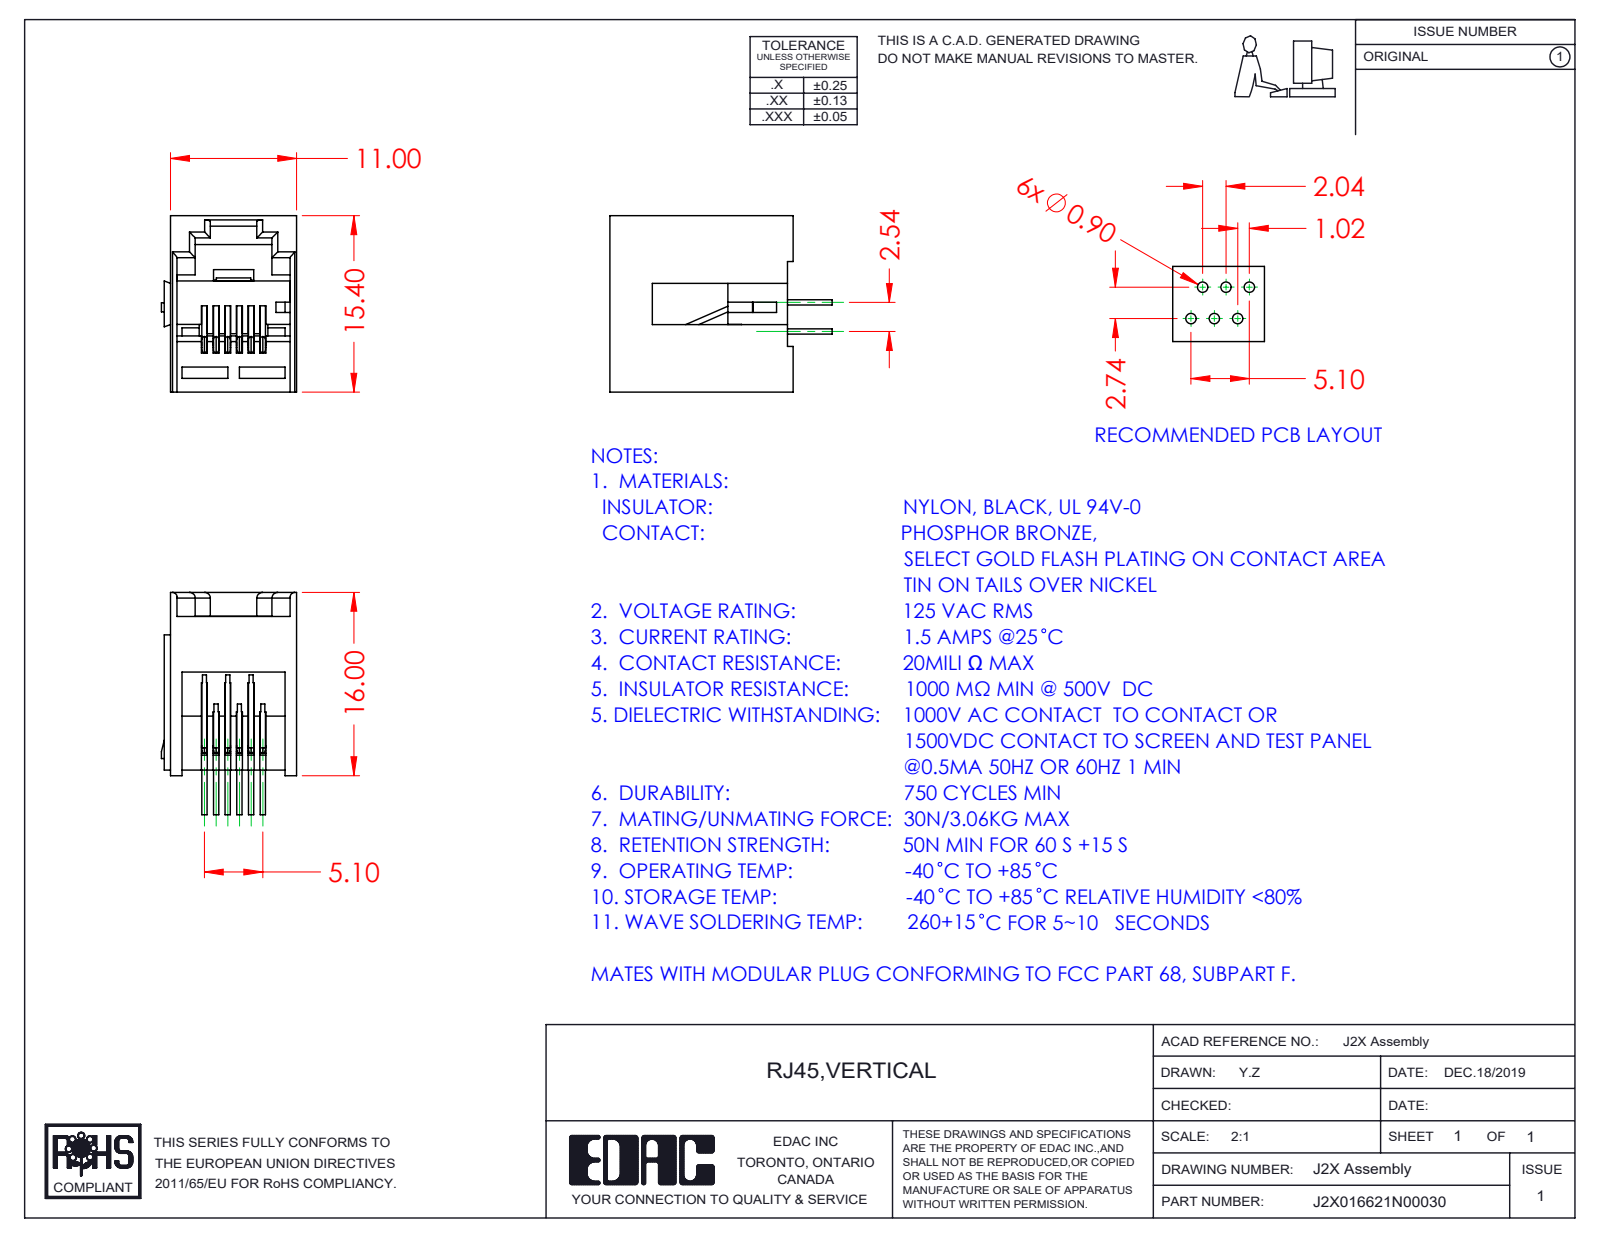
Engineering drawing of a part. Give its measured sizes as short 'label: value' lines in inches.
name: J2X016621N00030; 2X Contact Lock; 2X Insulator; 2X Contacts
written by: SolidWorks 2016 (CONFIG_CONTROL_DESIGN)
unit: in
bodies: 8 solids, 466 faces (333 planar, 97 cylindrical, 36 other)
size: 0.764 × 0.606 × 0.465
volume: 0.074 in³; area: 4.408 in²
bosses: 24× ⌀0.018
rounds: 7× R0.02, 2× R0.006, 2× R0.012, 2× R0.016, 1× R0.008
face distances: 0.039, 0.433, 0.08, 0.04, 0.02, 0.022, 0.02, 0.394, 0.472, 0.411
